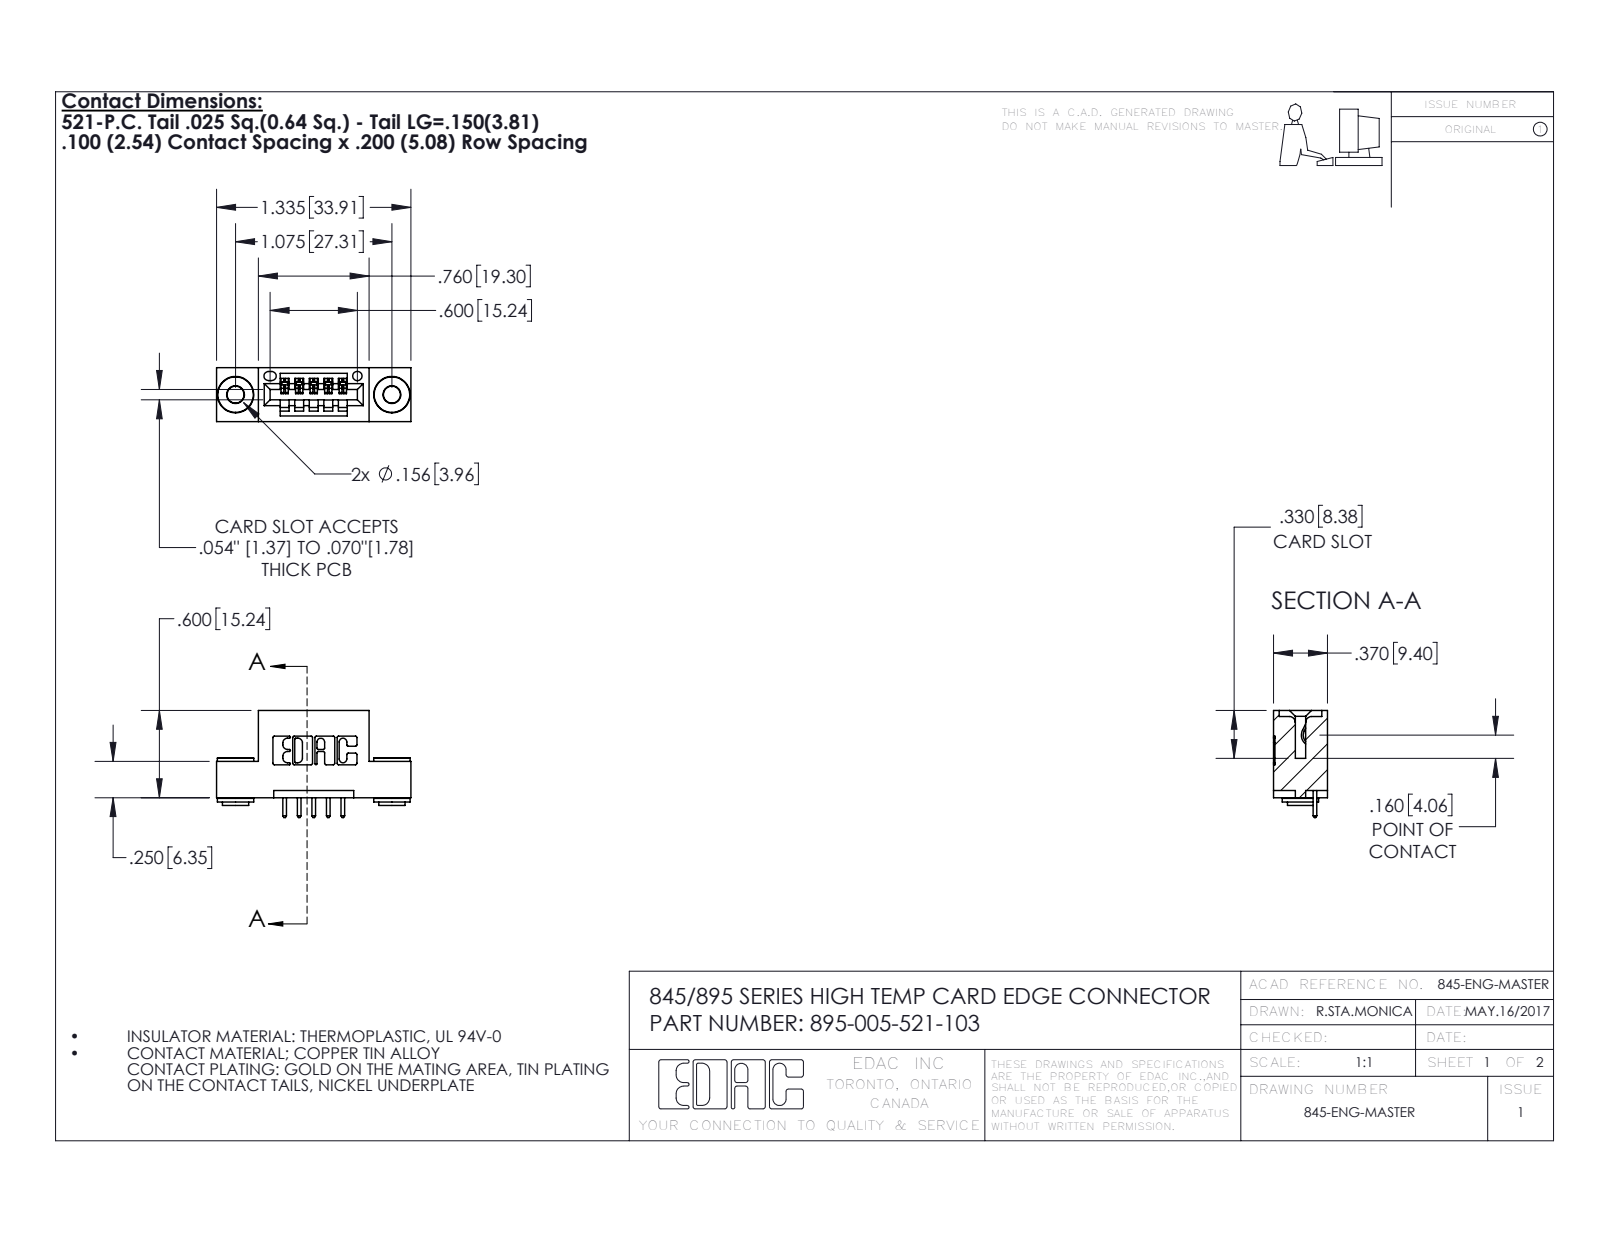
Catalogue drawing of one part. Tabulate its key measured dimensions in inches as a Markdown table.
| quantity | value |
| --- | --- |
| part name | 345-292-001_345-293-121; 345-250-002_345-250-002-102; 345 Part_Flush Mounting Lugs - 0.156 Dia-TH; 395-005-521-103 |
| STEP written by | SolidWorks 2016 (CONFIG_CONTROL_DESIGN) |
| units | inches |
| bodies | 8 solids, 454 faces (290 planar, 156 cylindrical, 8 other) |
| overall size | 1.335 × 0.737 × 0.37 |
| volume | 0.178 in³ |
| surface area | 5.487 in² |
| round holes (diameter × count) | 0.116 × 2, 0.156 × 2, 0.064 × 1 |
| round bosses / shafts (diameter × count) | 0.25 × 2, 0.18 × 2, 0.136 × 2 |
| partial cylindrical surfaces (radius × count) | 0.01 × 22, 0.006 × 10, 0.01 × 10, 0.007 × 6, 0.031 × 6, 0.026 × 3, 0.031 × 2, 0.04 × 2 |
| main face-to-face distances | 0.2, 0.37, 0.072, 0.298, 0.1, 0.25, 0.025, 0.35, 0.098, 0.272 |
| hole center spacings | 0.27, 0.847, 1.075 |
